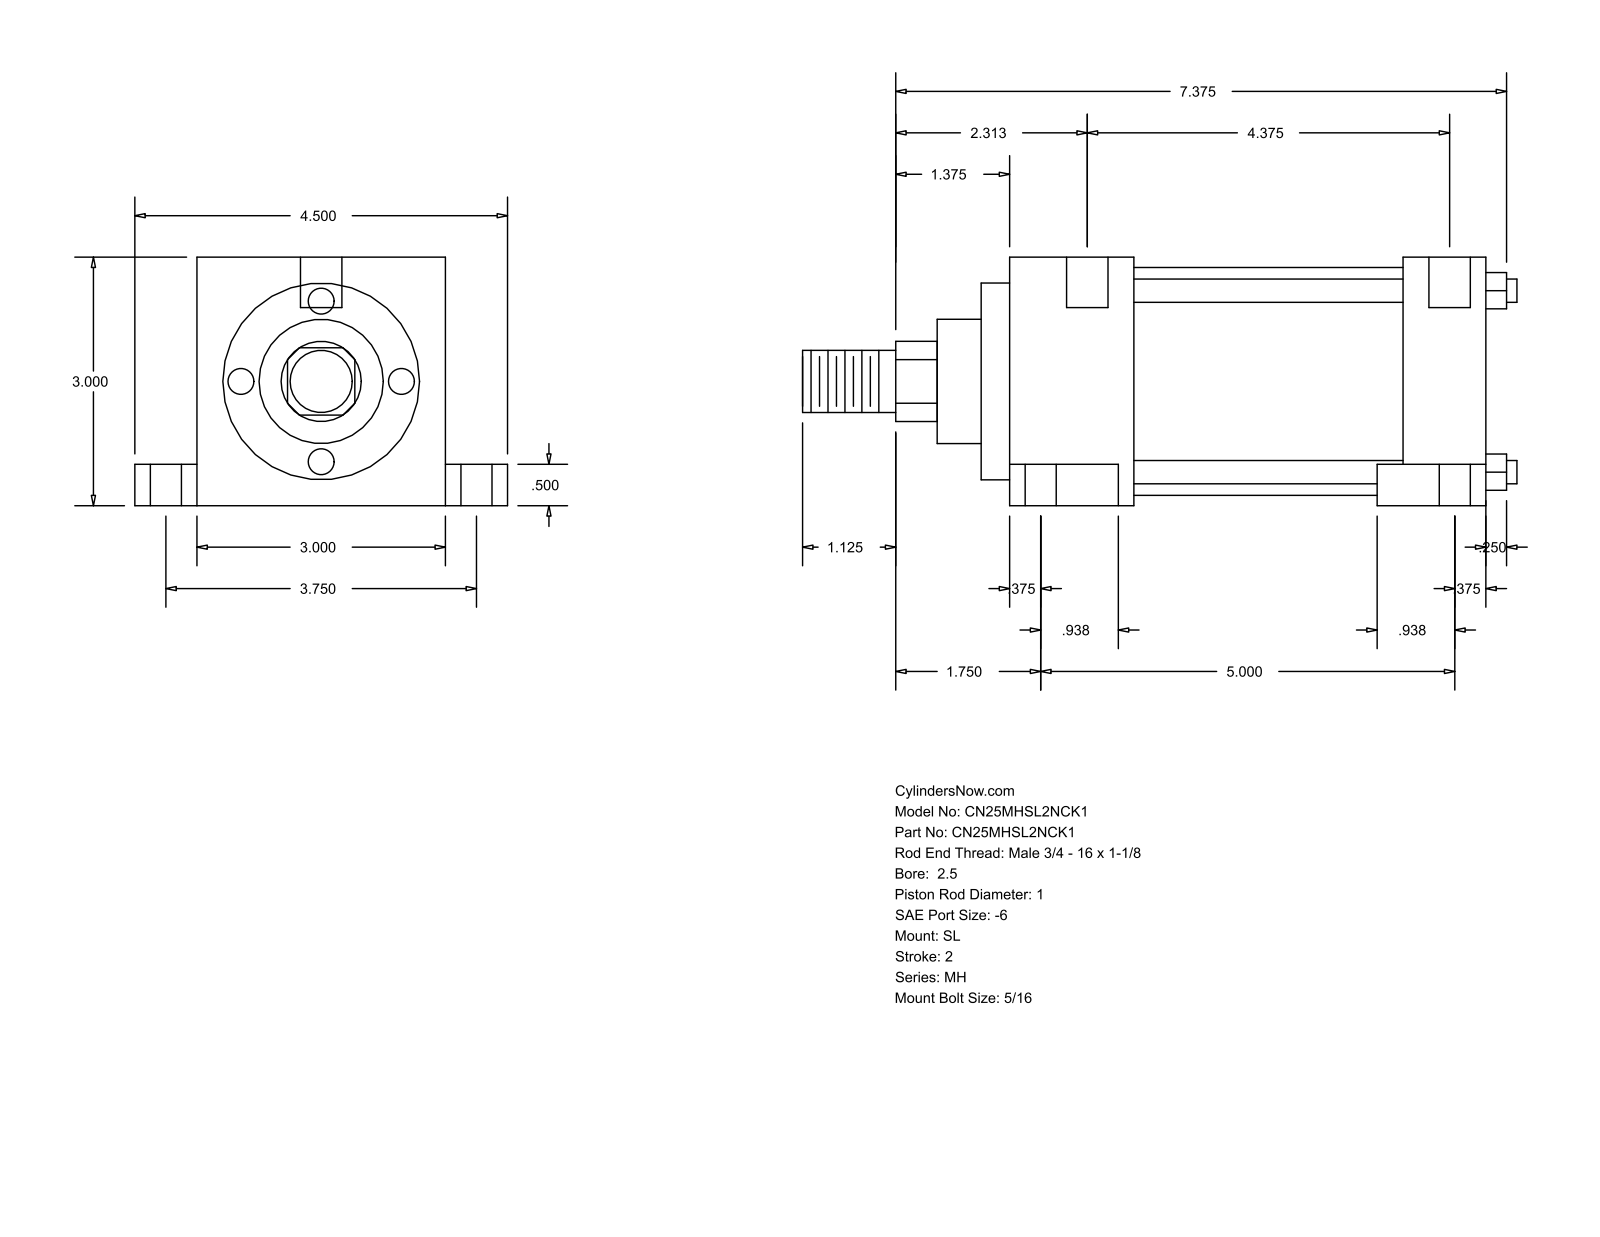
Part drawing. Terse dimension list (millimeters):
name: MH_SL__0250_1
written by: GSSL Pune (CONFIG_CONTROL_DESIGN)
unit: mm
bodies: 0 solids, 86 faces (61 planar, 25 cylindrical, 0 other)
size: 219.07 × 114.3 × 76.2
holes: 2× ⌀5.56, 2× ⌀9.53, 2× ⌀15.88, 1× ⌀12.7
bosses: 4× ⌀7.14, 1× ⌀69.85, 1× ⌀60.33, 1× ⌀38.1, 1× ⌀25.4, 1× ⌀19.05
rounds: 1× R12.29
face distances: 76.2, 25.4, 129.38, 154.78, 12.7, 63.5, 19.05, 95.25, 13.49, 142.87
hole spacings: 47.65, 3.18, 95.24
